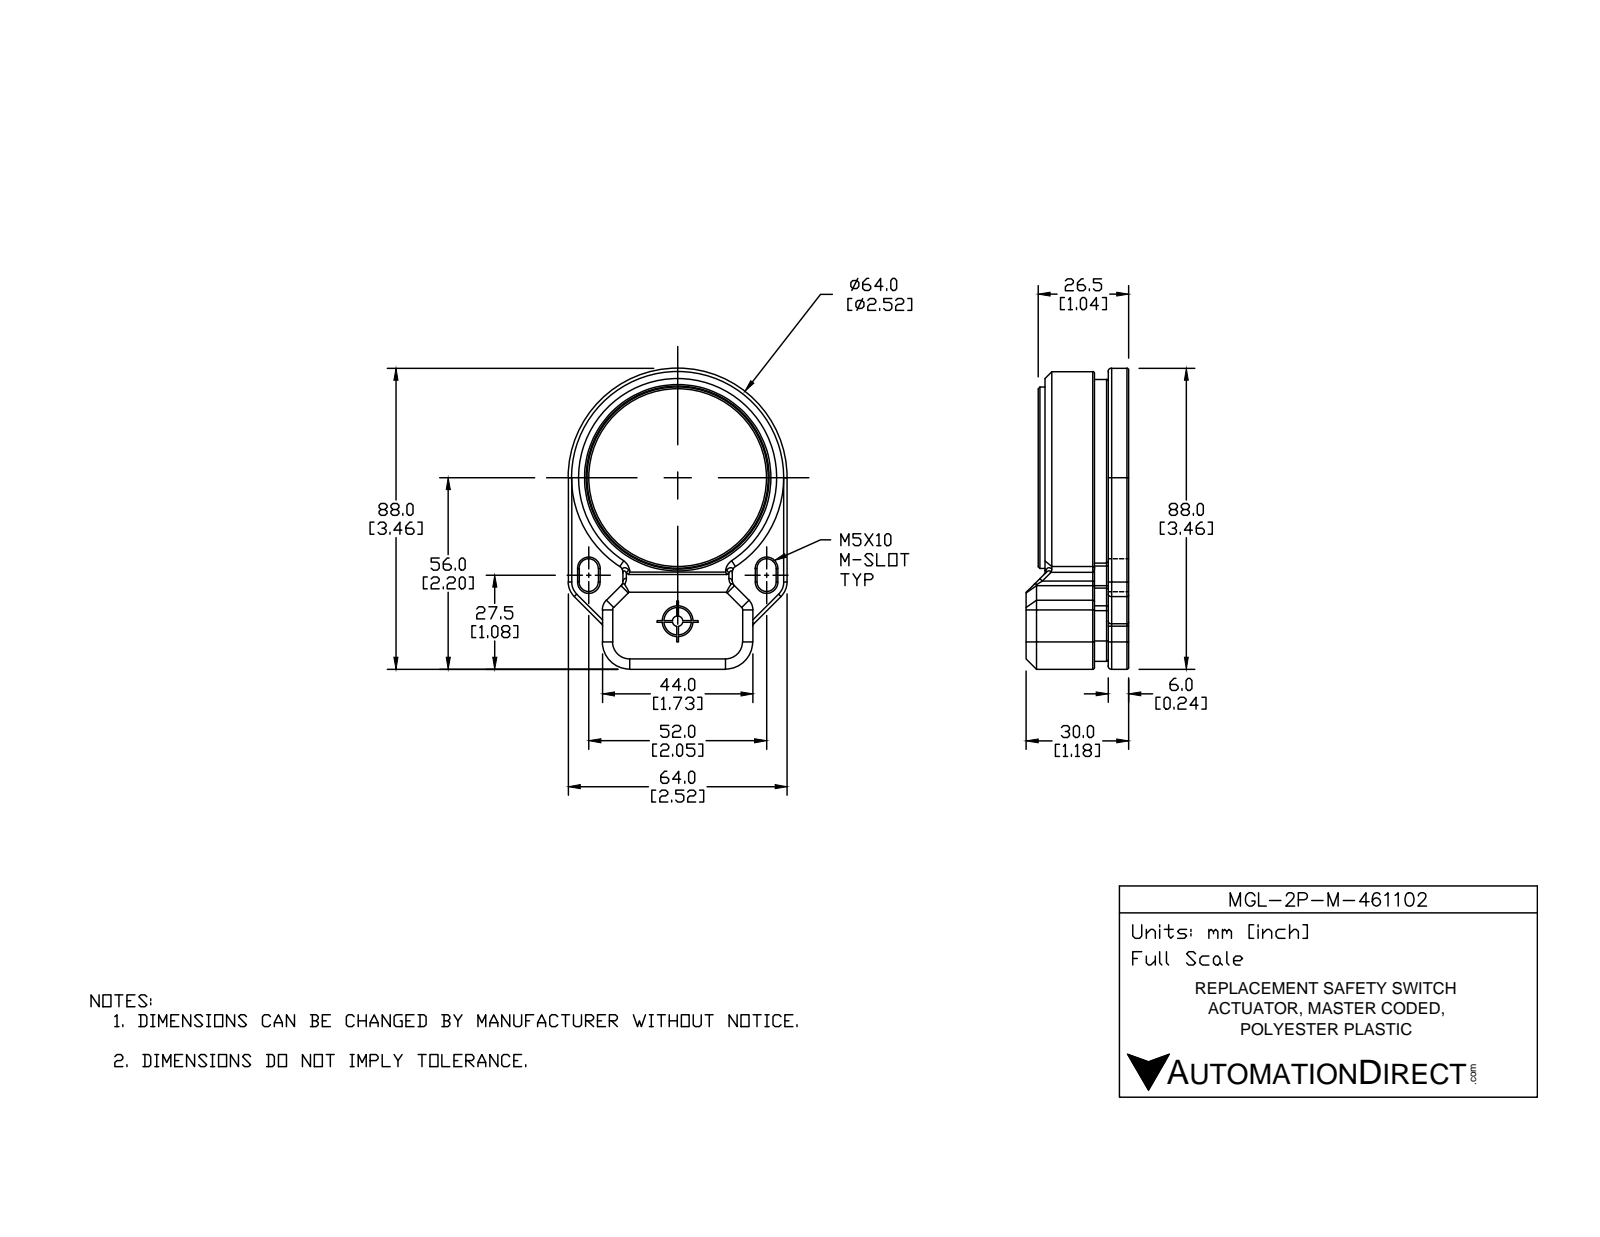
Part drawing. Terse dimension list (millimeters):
name: MGL-2P-M-461102
written by: SolidWorks 2017 (AUTOMOTIVE_DESIGN)
unit: mm
bodies: 5 solids, 504 faces (123 planar, 200 cylindrical, 181 other)
size: 88 × 64 × 30
volume: 77 720 mm³; area: 44 380 mm²
holes: 6× ⌀8, 2× ⌀4, 2× ⌀17, 1× ⌀5, 1× ⌀6.5, 1× ⌀8.2, 1× ⌀9, 1× ⌀10.5, 1× ⌀23.5, 1× ⌀53.5, 1× ⌀55.4, 1× ⌀58
bosses: 1× ⌀62, 1× ⌀57.4, 1× ⌀53, 1× ⌀23, 1× ⌀14, 1× ⌀13, 1× ⌀12, 1× ⌀10.2
rounds: 42× R0.5, 29× R1, 12× R2, 7× R0.6, 5× R6, 4× R2.8, 2× R4, 2× R4.8
face distances: 10.5, 6, 16.5, 2.5, 10, 8, 6.5, 14, 1.5, 7.5
hole spacings: 19.5, 27.6, 13.9, 30.4, 39, 46.3, 47.4, 48.8
